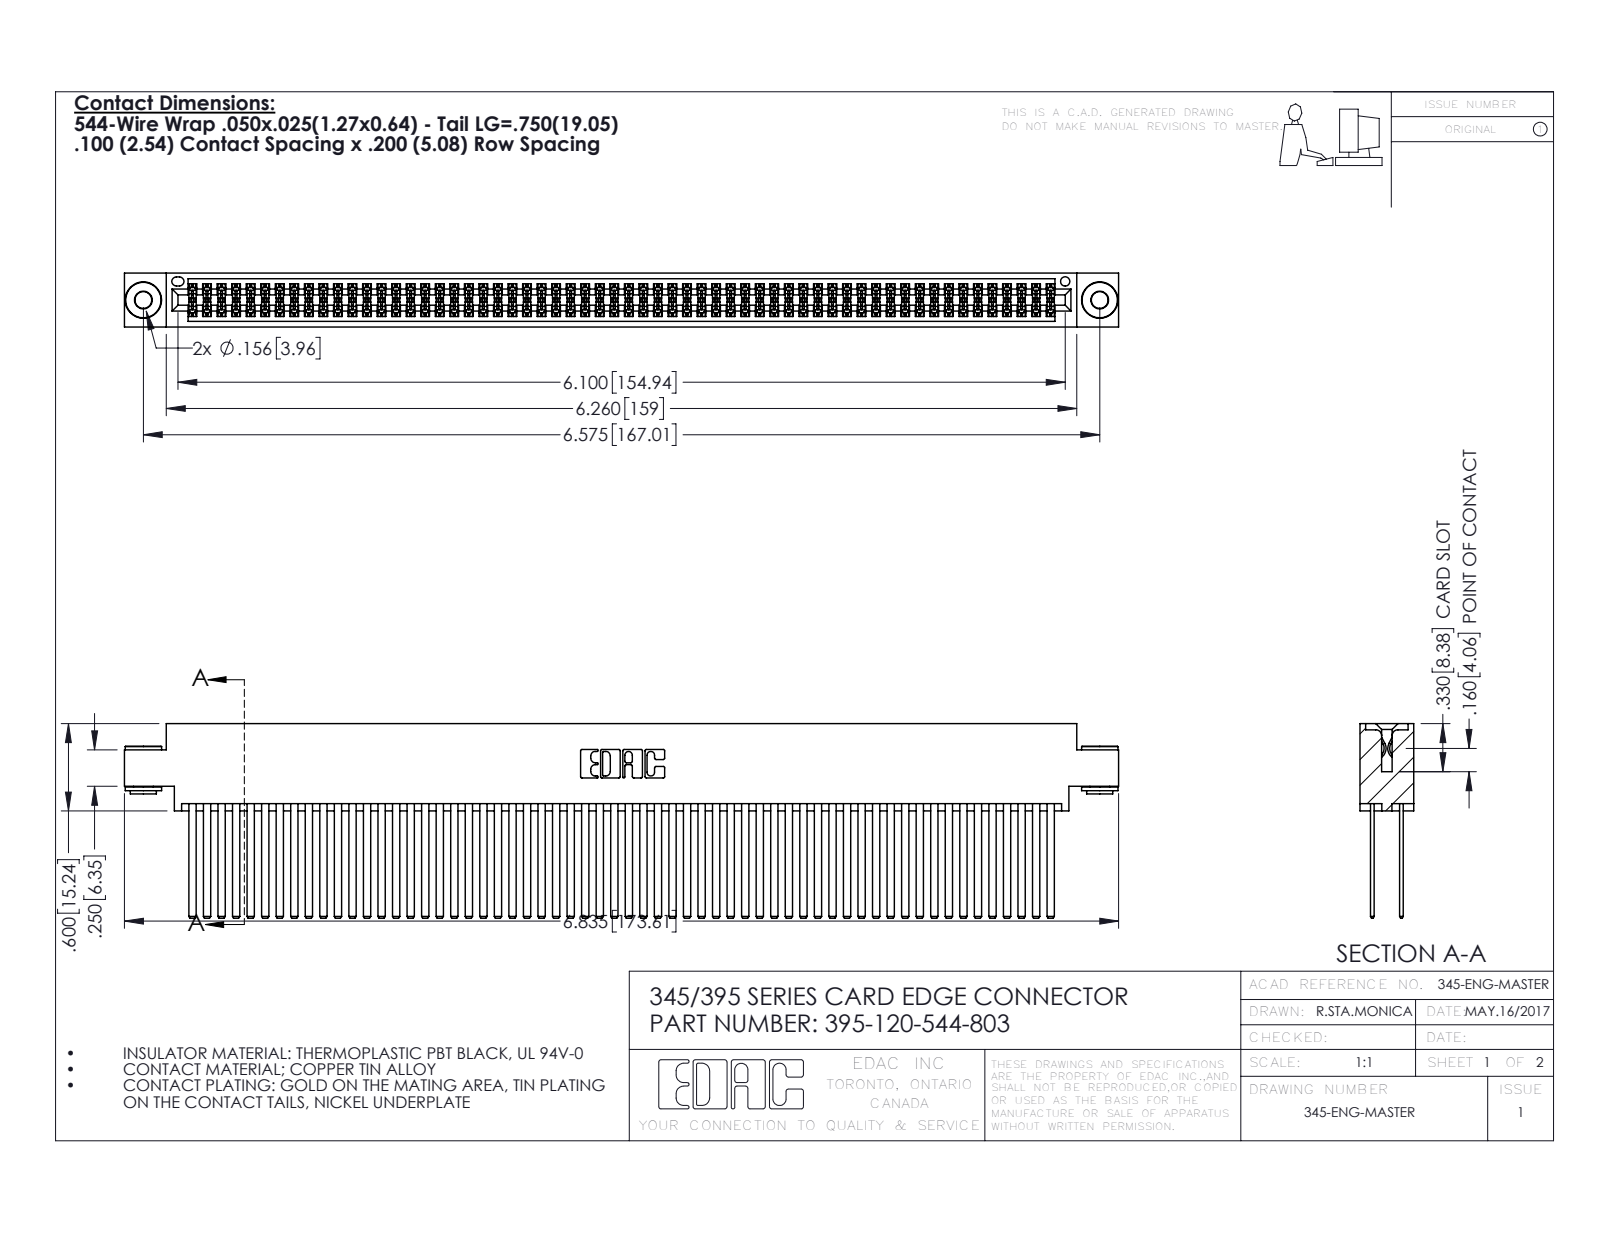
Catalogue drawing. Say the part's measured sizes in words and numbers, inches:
The part is named "395-120-544-803; 345-292-001_345-293-144; 345 Part_0.170 Offset - 0.156 Dia-TH; 345-250-002_345-250-002-102". Its 3-D file was written by "SolidWorks 2016 (CONFIG_CONTROL_DESIGN)". It is 123 solids with 5448 faces: 3574 planar, 1866 cylindrical and 8 other. Overall it measures 6.835 by 1.337 by 0.37 inches. Its volume is 1.136 cubic inches and its surface area 51.38 square inches. Round holes: 2 of diameter 0.116, 2 of diameter 0.156, 1 of diameter 0.064. Round bosses or shafts: 2 of diameter 0.25, 2 of diameter 0.18, 2 of diameter 0.136. Partial cylindrical surfaces (rounded edges, fillets, slot ends): 180 of radius 0.006, 22 of radius 0.01, 6 of radius 0.007, 6 of radius 0.031, 3 of radius 0.026, 2 of radius 0.014, 2 of radius 0.019, 2 of radius 0.022. The main face-to-face distances are 0.2, 0.025, 0.072, 0.098, 0.272, 0.298, 0.225, 0.175, 0.37, 0.15. The hole center spacings are 0.27, 6.339, 6.575.
